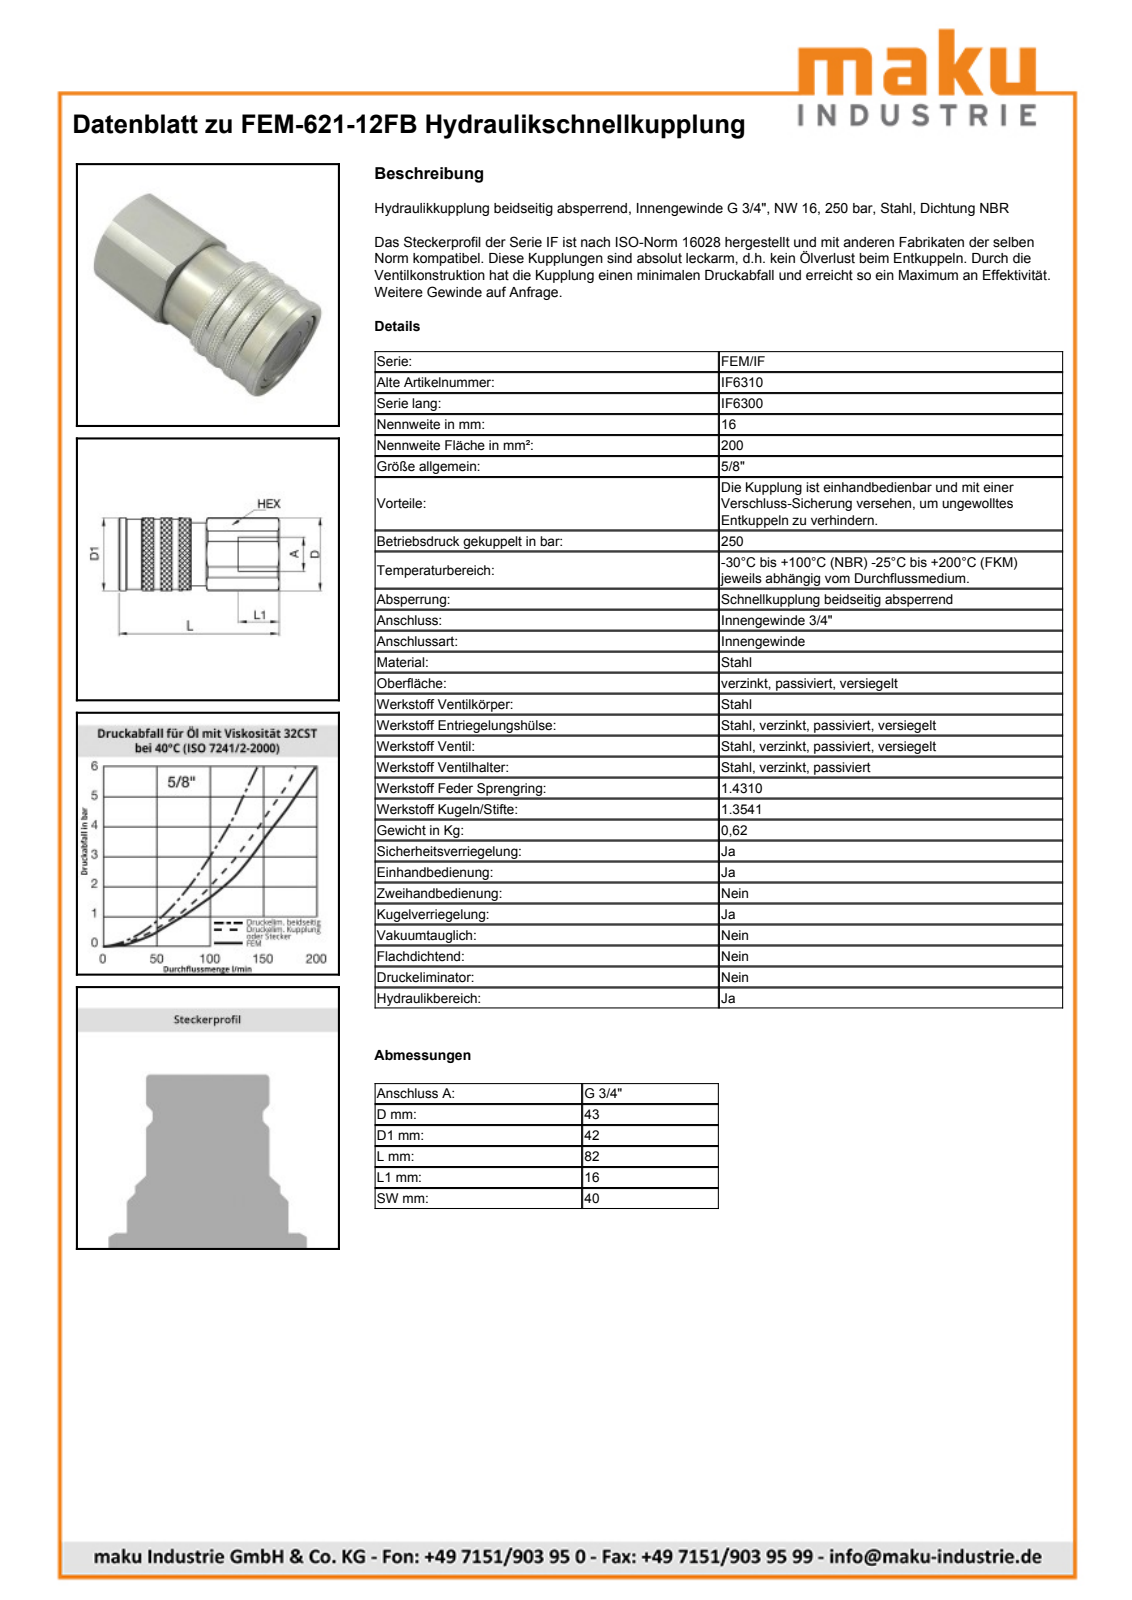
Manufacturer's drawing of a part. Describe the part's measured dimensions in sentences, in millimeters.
The part is named "FEM-621-12FB". Its 3-D file was written by "SolidWorks 2009 (AUTOMOTIVE_DESIGN)". It is 1 solid with 119 faces: 31 planar, 48 cylindrical and 40 other. Overall it measures 81.6 by 43 by 42 millimeters. Its volume is 96 634 cubic millimeters and its surface area 16 825 square millimeters. Round holes: 1 of diameter 17.8, 1 of diameter 24.12, 1 of diameter 27.2, 1 of diameter 33.3, 1 of diameter 37.3. Round bosses or shafts: 1 of diameter 42, 1 of diameter 40.7, 1 of diameter 36.7, 1 of diameter 35.52, 1 of diameter 32.5, 1 of diameter 27, 1 of diameter 17.5, 1 of diameter 3.5. Partial cylindrical surfaces (rounded edges, fillets, slot ends): 2 of radius 0.5, 1 of radius 21.5. The main face-to-face distances are 40, 81.6, 81.2, 0.4, 18.38, 62.82, 63.22, 35, 16.62, 46.2.
